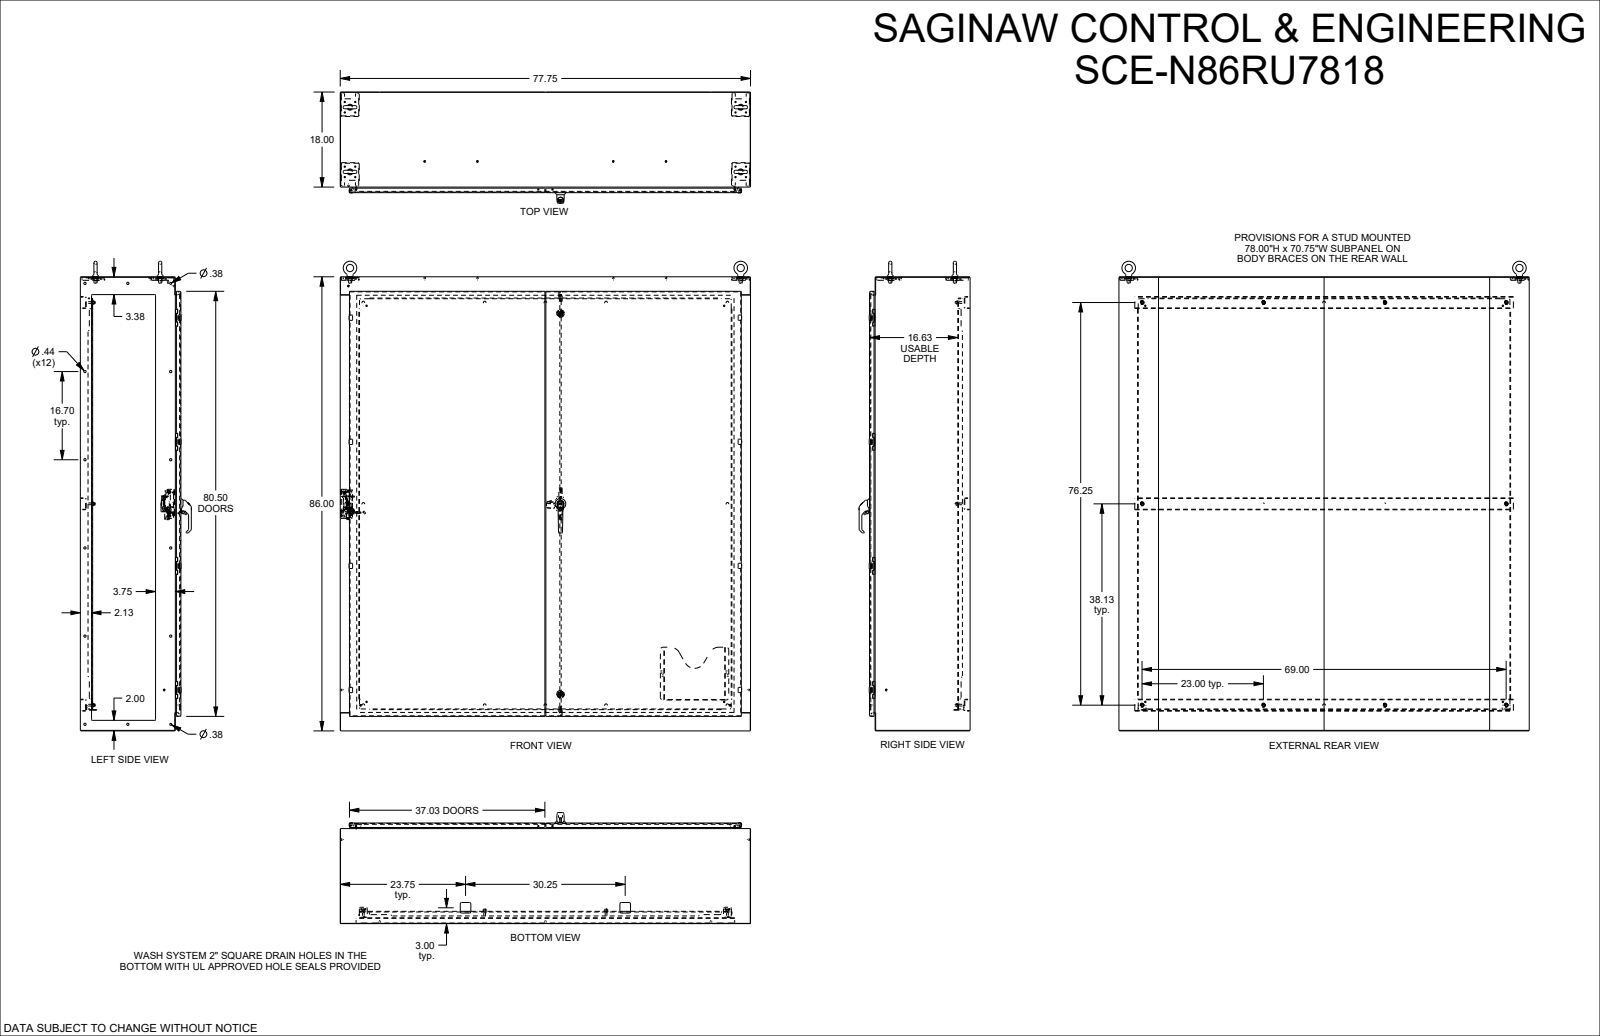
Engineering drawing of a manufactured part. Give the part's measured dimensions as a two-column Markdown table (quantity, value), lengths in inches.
| quantity | value |
| --- | --- |
| part name | SCE-N86RU7818_REV1 |
| STEP written by | SolidWorks 2023 (AUTOMOTIVE_DESIGN) |
| units | inches |
| bodies | 34 solids, 5069 faces (2403 planar, 1662 cylindrical, 1004 other) |
| overall size | 88.945 × 77.75 × 21.046 |
| volume | 2 164 in³ |
| surface area | 41 506 in² |
| round holes (diameter × count) | 0.25 × 18, 0.375 × 18, 0.205 × 16, 0.244 × 16, 0.437 × 12, 0.04 × 8, 0.218 × 8, 0.17 × 4, 0.256 × 4, 0.875 × 4, 0.206 × 2, 0.343 × 2 |
| round bosses / shafts (diameter × count) | 0.17 × 24, 0.25 × 16, 0.24 × 16, 0.645 × 12, 0.196 × 10, 1.173 × 4, 0.6 × 4, 1.4 × 2 |
| partial cylindrical surfaces (radius × count) | 0.03 × 102, 0.015 × 88, 0.125 × 67, 0.04 × 41, 0.167 × 38, 0.062 × 34, 0.063 × 32, 0.229 × 32 |
| main face-to-face distances | 0.104, 18.954, 18.85, 19.058, 85.896, 17.896, 1.058, 86, 85.792, 77.646 |
| hole center spacings | 23.5, 1.979, 47, 72.868, 1.4, 76.525, 16.7, 23.302 |
